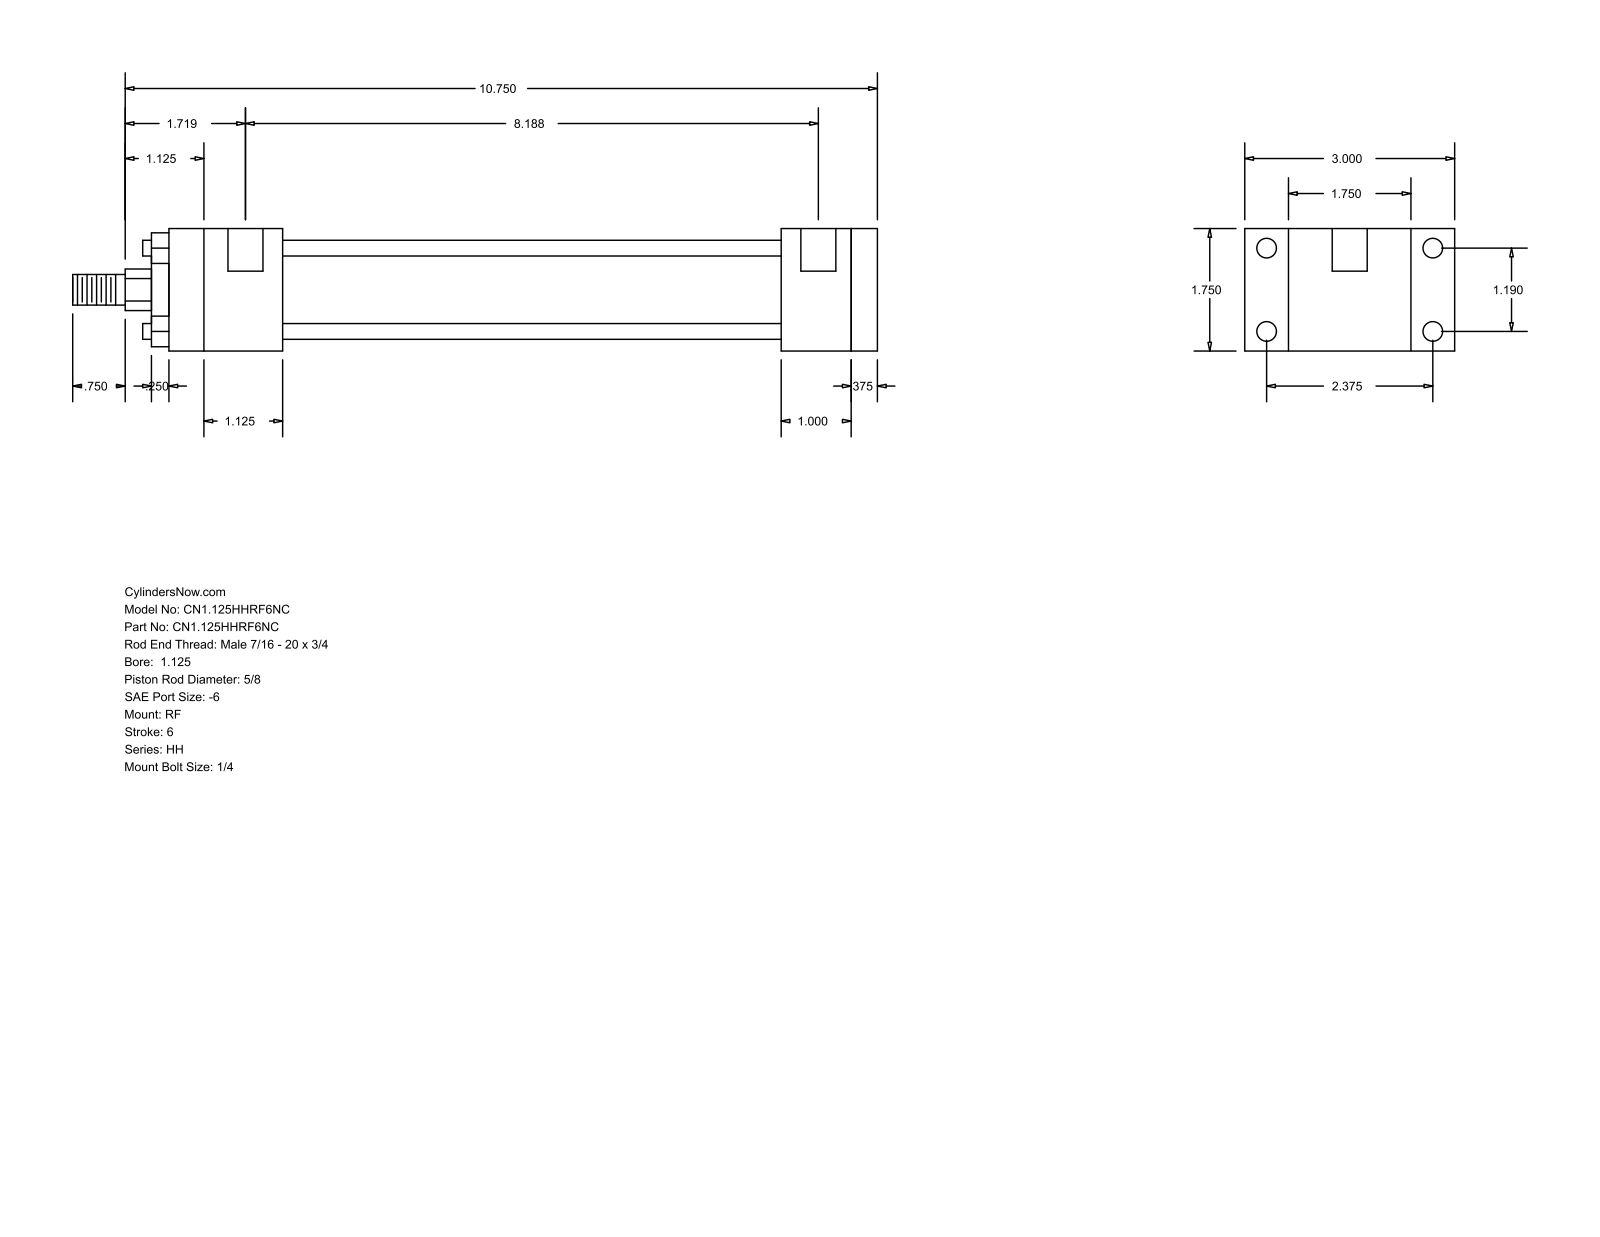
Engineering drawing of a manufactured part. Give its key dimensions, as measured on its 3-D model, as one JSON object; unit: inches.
{"part_name": "HH_RF__0112_0.625", "step_written_by": "GSSL Pune (CONFIG_CONTROL_DESIGN)", "units": "inches", "bodies": {"solids": 0, "faces": 92, "planar": 64, "cylindrical": 28, "other": 0}, "overall_size": [11.5, 3, 1.75], "round_holes": [[0.219, 4], [0.281, 4], [0.5, 2]], "round_bosses_or_shafts": [[0.225, 4], [1.375, 1], [1.125, 1], [0.625, 1], [0.437, 1]], "partial_cylinders_radius": [[0.297, 1]], "face_to_face_distances": [1.75, 0.375, 10.125, 1, 1.375, 0.625, 8.125, 8.5, 7.125, 1.625], "hole_center_spacings": [1.19, 2.375, 2.656, 8.063, 0.125, 8.187]}
